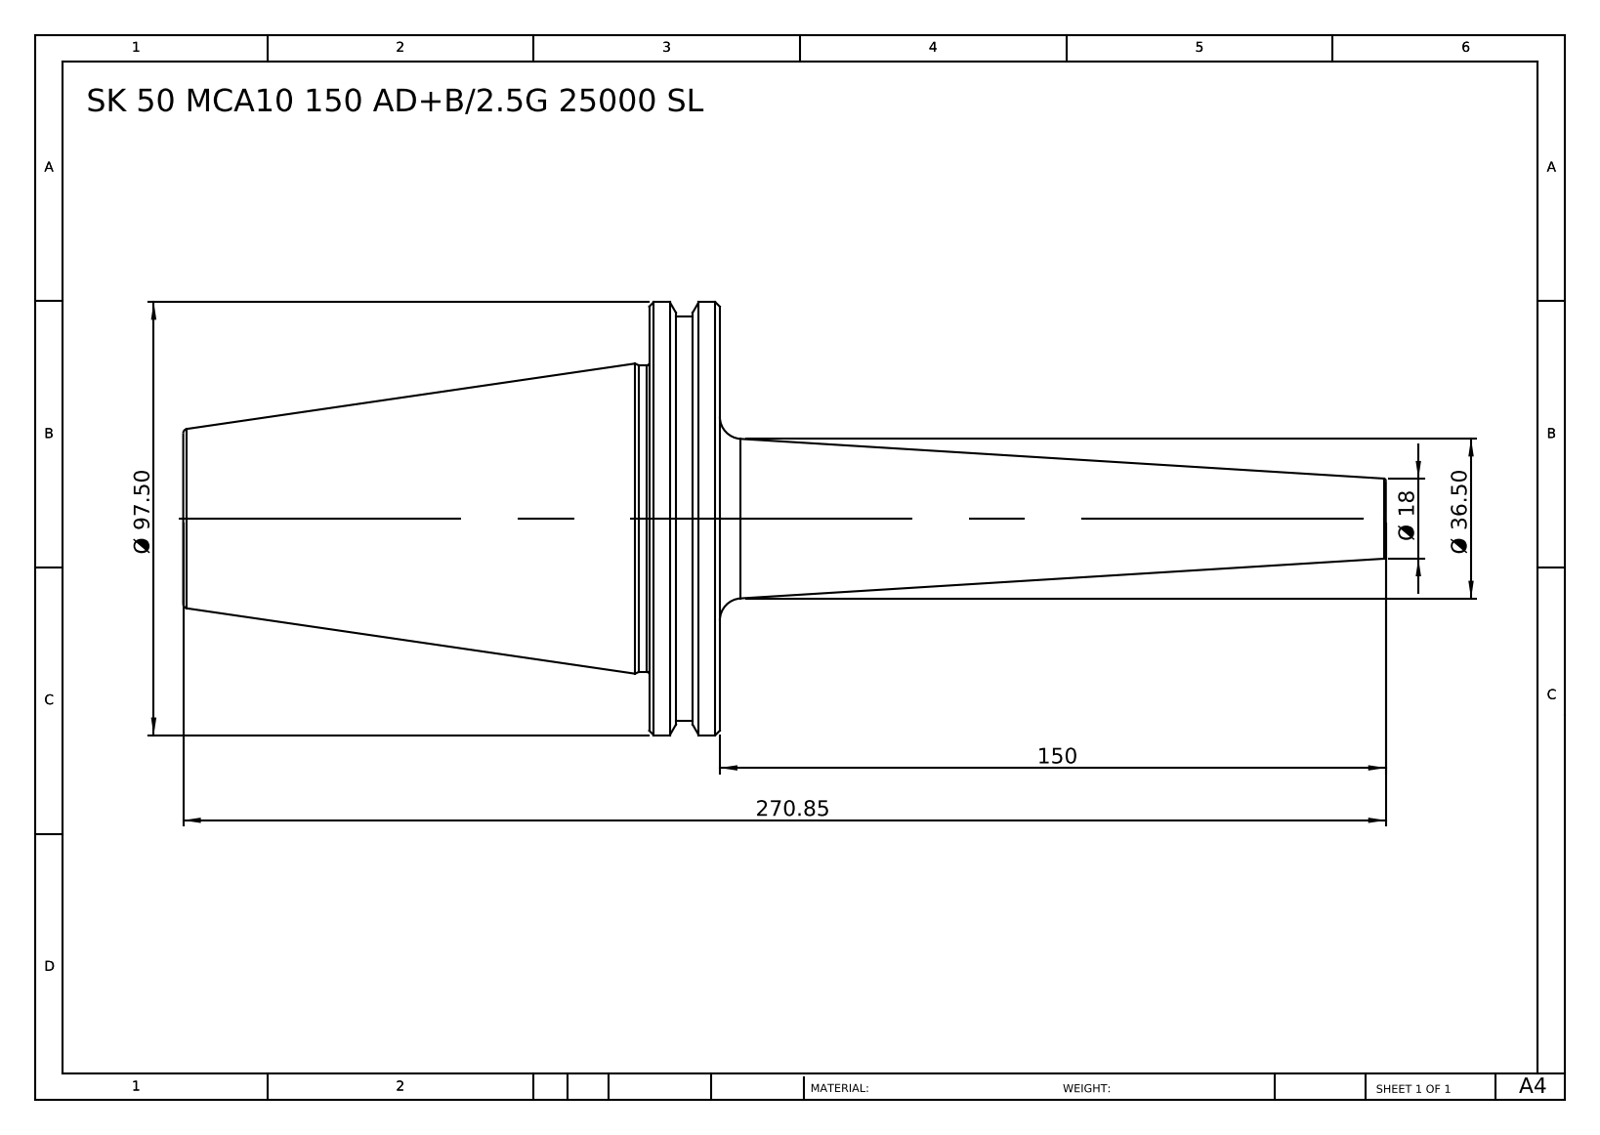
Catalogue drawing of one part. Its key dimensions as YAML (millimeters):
part_name: "SK 50 MCA10 150 AD+B-2.5G25000 SL"
step_written_by: "SolidWorks 2014 (CONFIG_CONTROL_DESIGN)"
units: millimeters
bodies: {solids: 1, faces: 36, planar: 6, cylindrical: 8, other: 22}
overall_size: [270.85, 97.5, 97.5]
volume: 464944
surface_area: 48462
round_bosses_or_shafts:
  - {diameter: 97.5, count: 1}
  - {diameter: 91, count: 1}
  - {diameter: 69, count: 1}
face_to_face_distances: [15.9, 120.85, 104.95, 6.12, 9.78, 114.73, 9.88, 3.76, 6.02, 110.97]
